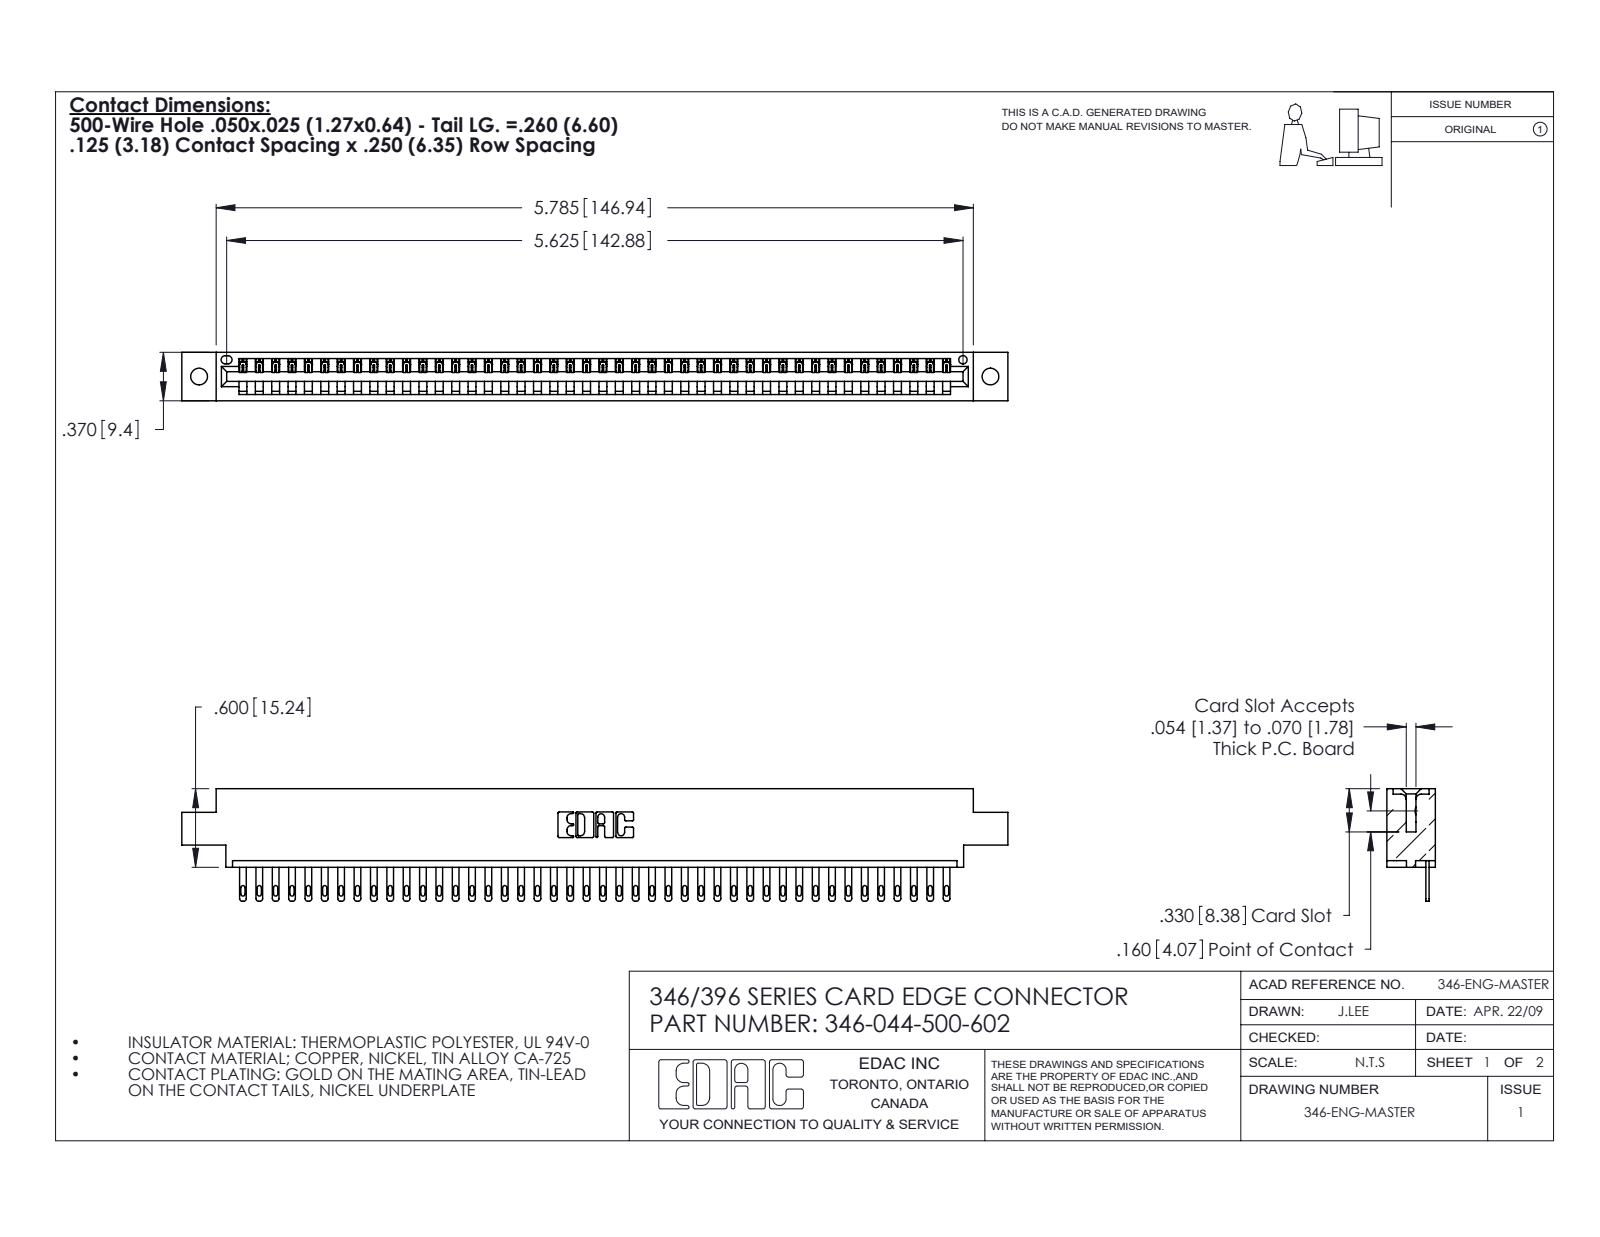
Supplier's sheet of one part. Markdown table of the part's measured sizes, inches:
| quantity | value |
| --- | --- |
| part name | 346-044-500-602; 345-292-001_345-293-100; 346 Part_0.170 Offset - 0.128 Dia |
| STEP written by | SolidWorks 2020 (CONFIG_CONTROL_DESIGN) |
| units | inches |
| bodies | 45 solids, 2502 faces (1576 planar, 926 cylindrical, 0 other) |
| overall size | 6.31 × 0.86 × 0.37 |
| volume | 0.927 in³ |
| surface area | 29.45 in² |
| round holes (diameter × count) | 0.128 × 2, 0.064 × 1 |
| partial cylindrical surfaces (radius × count) | 0.006 × 88, 0.016 × 88, 0.02 × 88, 0.01 × 22, 0.007 × 6, 0.031 × 6, 0.026 × 3, 0.031 × 2 |
| main face-to-face distances | 0.048, 0.322, 0.37, 0.25, 0.072, 0.298, 0.025, 0.148, 0.222, 0.1 |
| hole center spacings | 0.246, 5.836, 6.045 |
